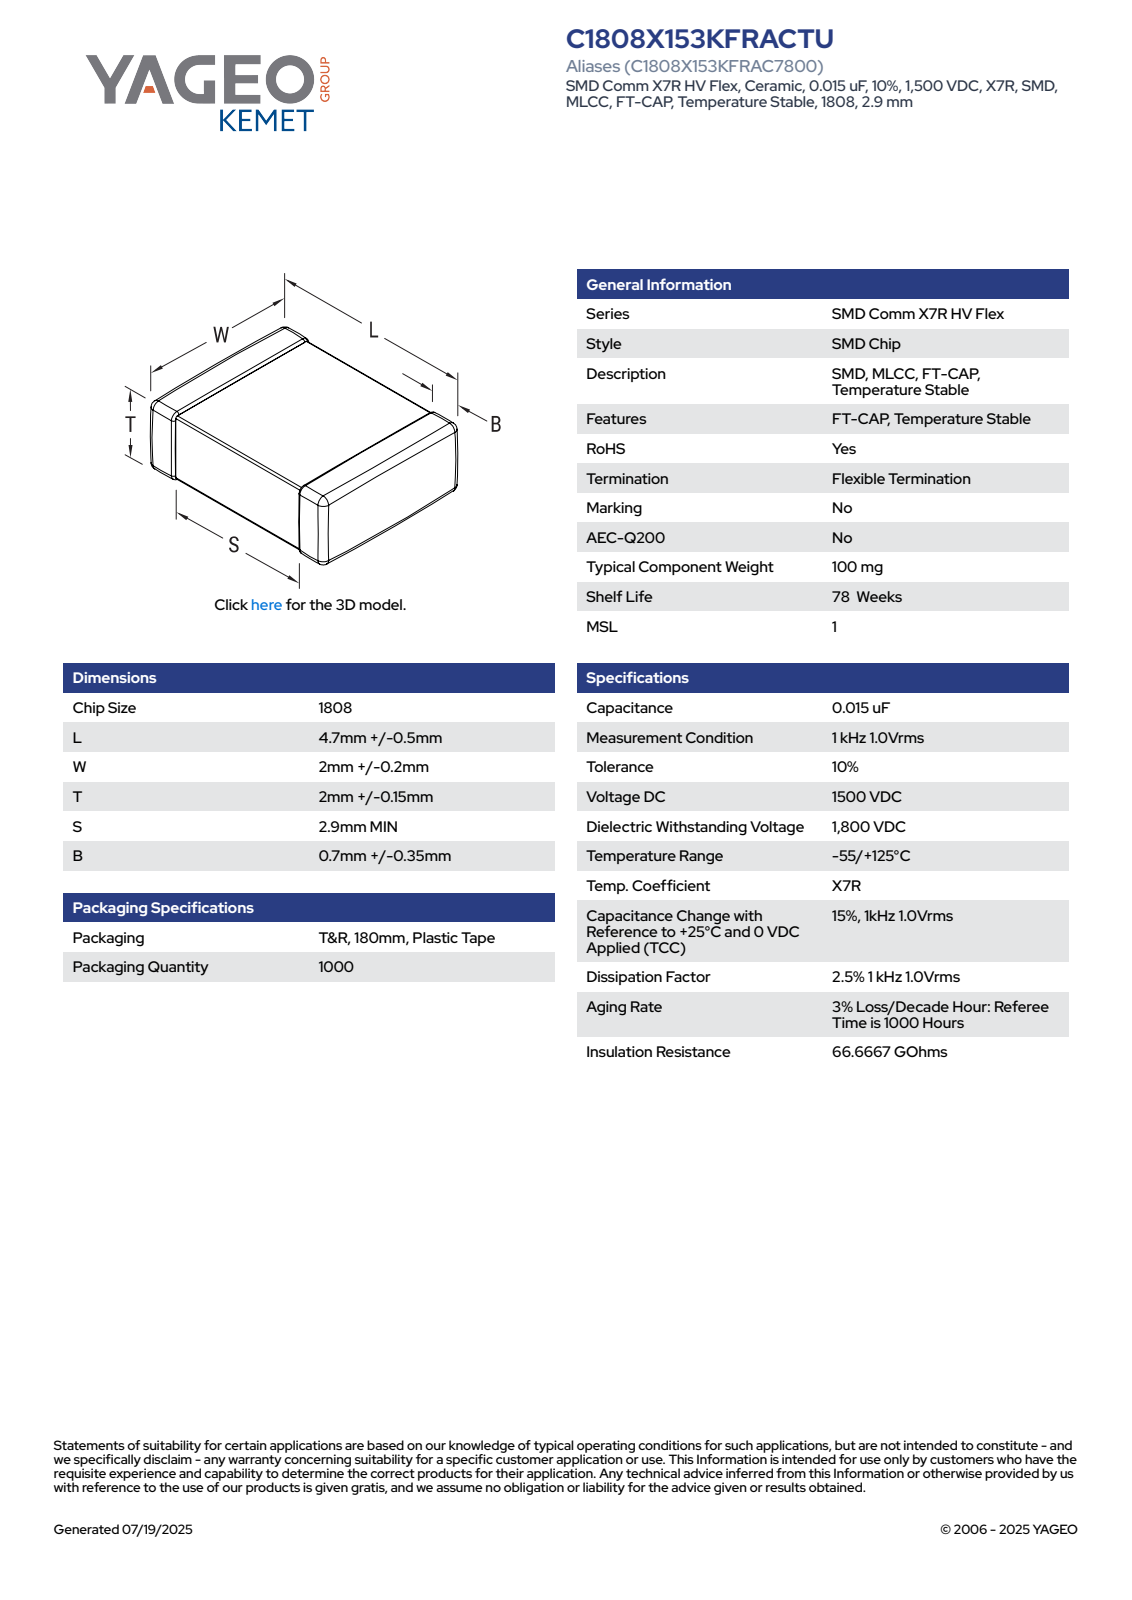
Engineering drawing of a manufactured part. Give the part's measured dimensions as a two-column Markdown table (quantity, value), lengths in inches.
| quantity | value |
| --- | --- |
| part name | CCS_CCSTD_1808_L5.2W2.2T2.15B0.7 |
| STEP written by | SolidWorks 2021 (AUTOMOTIVE_DESIGN) |
| units | inches |
| bodies | 4 solids, 125 faces (71 planar, 38 cylindrical, 16 other) |
| overall size | 0.205 × 0.087 × 0.085 |
| volume | 0.001 in³ |
| surface area | 0.084 in² |
| main face-to-face distances | 0.083, 0.085, 0.081, 0.205, 0.087, 0.083, 0.081, 0.013, 0.098, 0.107 |
